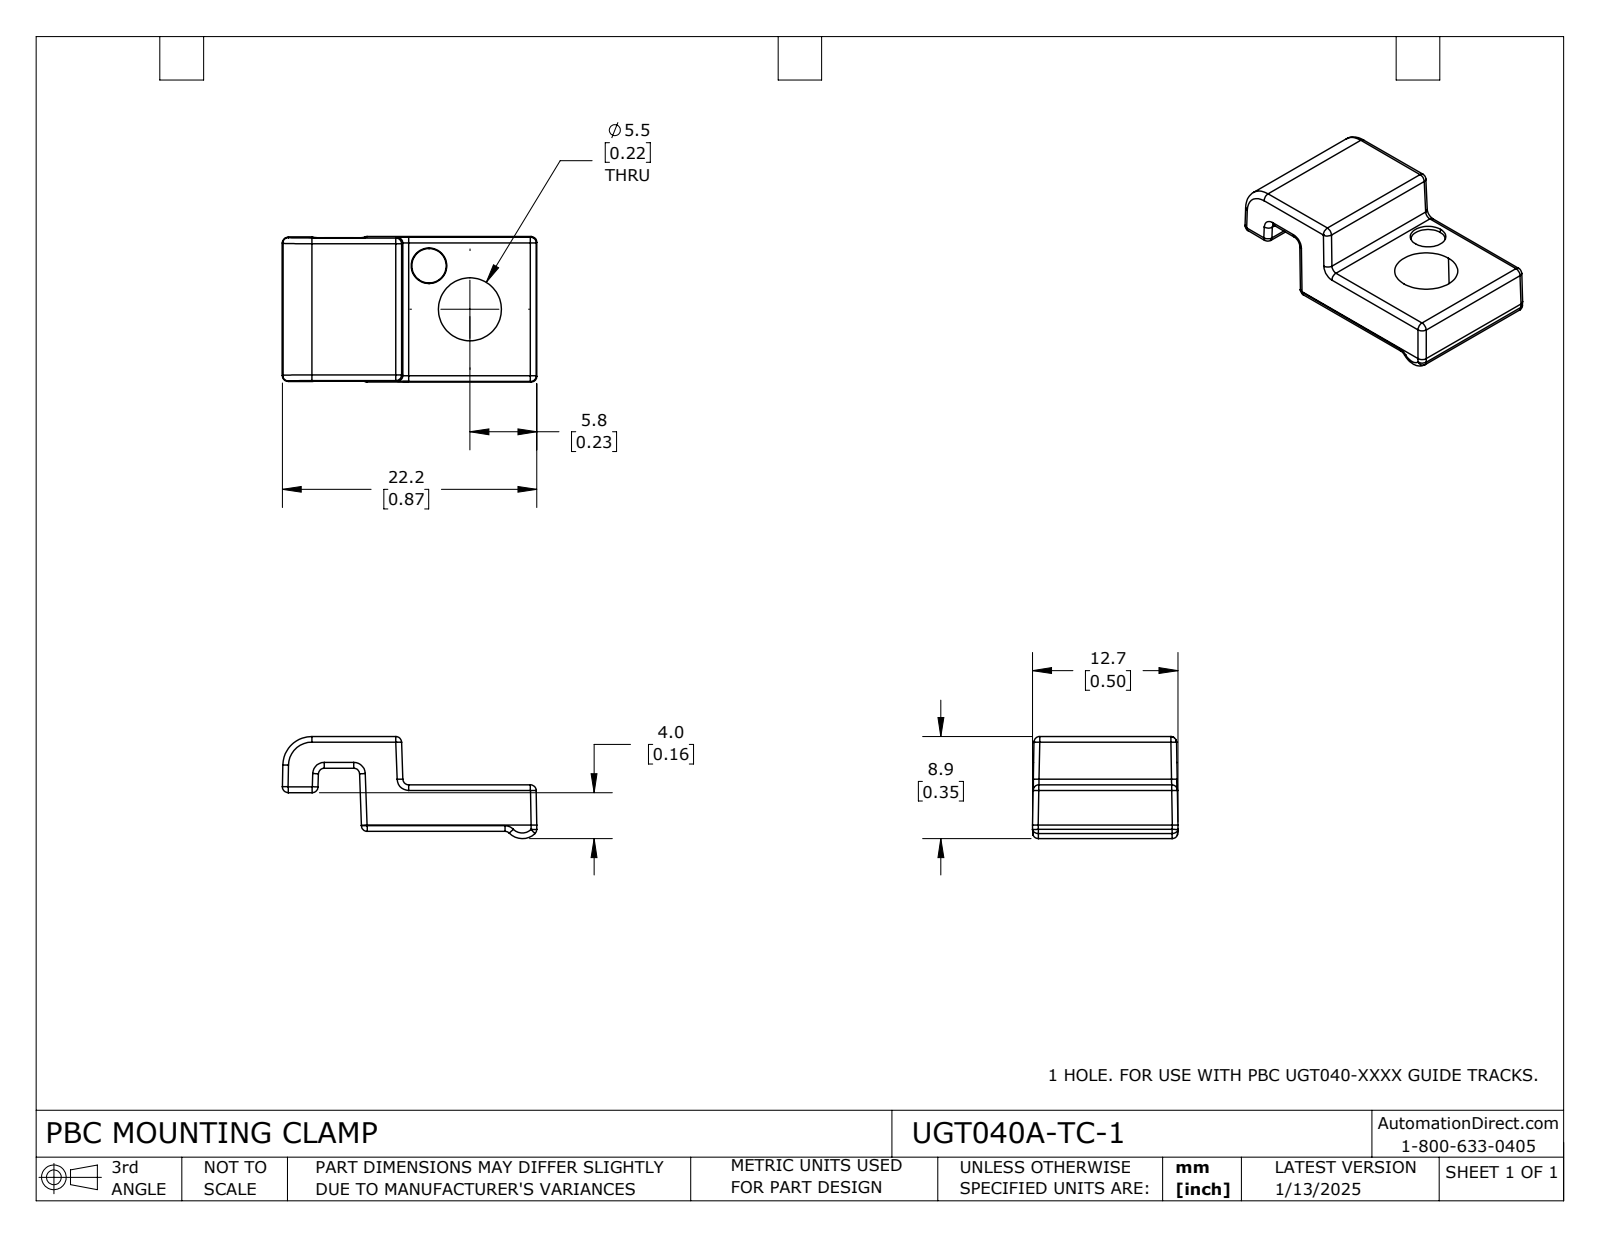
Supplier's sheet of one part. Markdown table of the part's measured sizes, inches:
| quantity | value |
| --- | --- |
| part name | UGT040A-TC-1 |
| STEP written by | SolidWorks 2023 (CONFIG_CONTROL_DESIGN) |
| units | inches |
| bodies | 1 solid, 81 faces (16 planar, 37 cylindrical, 28 other) |
| overall size | 0.875 × 0.5 × 0.351 |
| volume | 0.072 in³ |
| surface area | 1.532 in² |
| partial cylindrical surfaces (radius × count) | 0.02 × 24, 0.02 × 10, 0.062 × 1, 0.1 × 1 |
| main face-to-face distances | 0.16, 0.326, 0.166, 0.148, 0.217, 0.057, 0.109, 0.133, 0.027, 0.084 |
